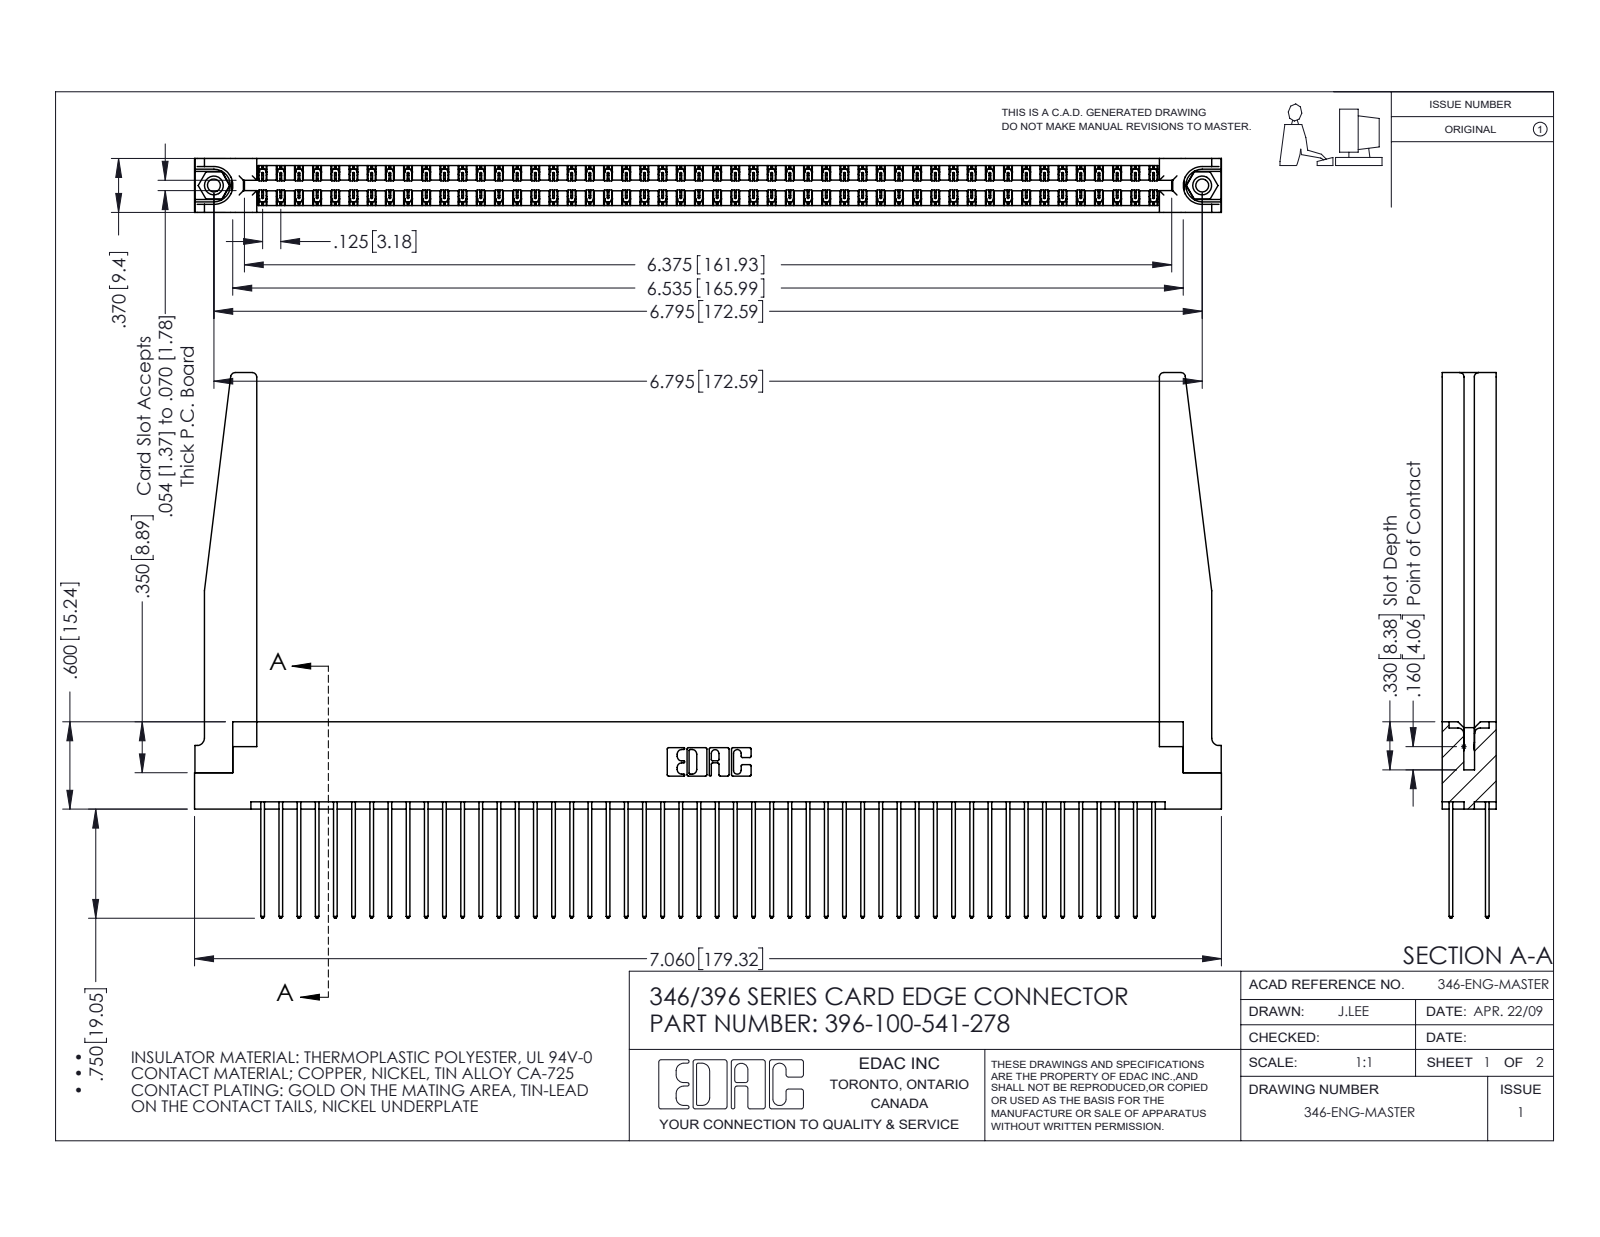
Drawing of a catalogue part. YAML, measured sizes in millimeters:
part_name: "346-220-078_345-220-078; 346 Part_Flush Mounting Lugs - 0.156 Dia-TH; 345-292-001_345-293-141; 345-250-001_345-250-001-102 (+1 more)"
step_written_by: "SolidWorks 2016 (CONFIG_CONTROL_DESIGN)"
units: millimeters
bodies: {solids: 105, faces: 5556, planar: 3718, cylindrical: 1786, other: 52}
overall_size: [179.3, 95.3, 9.4]
volume: 25020
surface_area: 34320
round_holes:
  - {diameter: 2.3, count: 2}
  - {diameter: 3.2, count: 2}
  - {diameter: 4, count: 2}
  - {diameter: 1.6, count: 1}
round_bosses_or_shafts:
  - {diameter: 3.9, count: 2}
partial_cylinders:
  - {radius: 0.2, count: 150}
  - {radius: 0.3, count: 100}
  - {radius: 0.3, count: 22}
  - {radius: 0.8, count: 8}
  - {radius: 0.2, count: 6}
  - {radius: 0.8, count: 6}
  - {radius: 0.7, count: 3}
  - {radius: 0.4, count: 2}
face_to_face_distances: [1.2, 8.2, 1.8, 9.4, 6.4, 7.6, 0.6, 7, 3.8, 3.8]
hole_center_spacings: [6.2, 167.3, 172.6]
